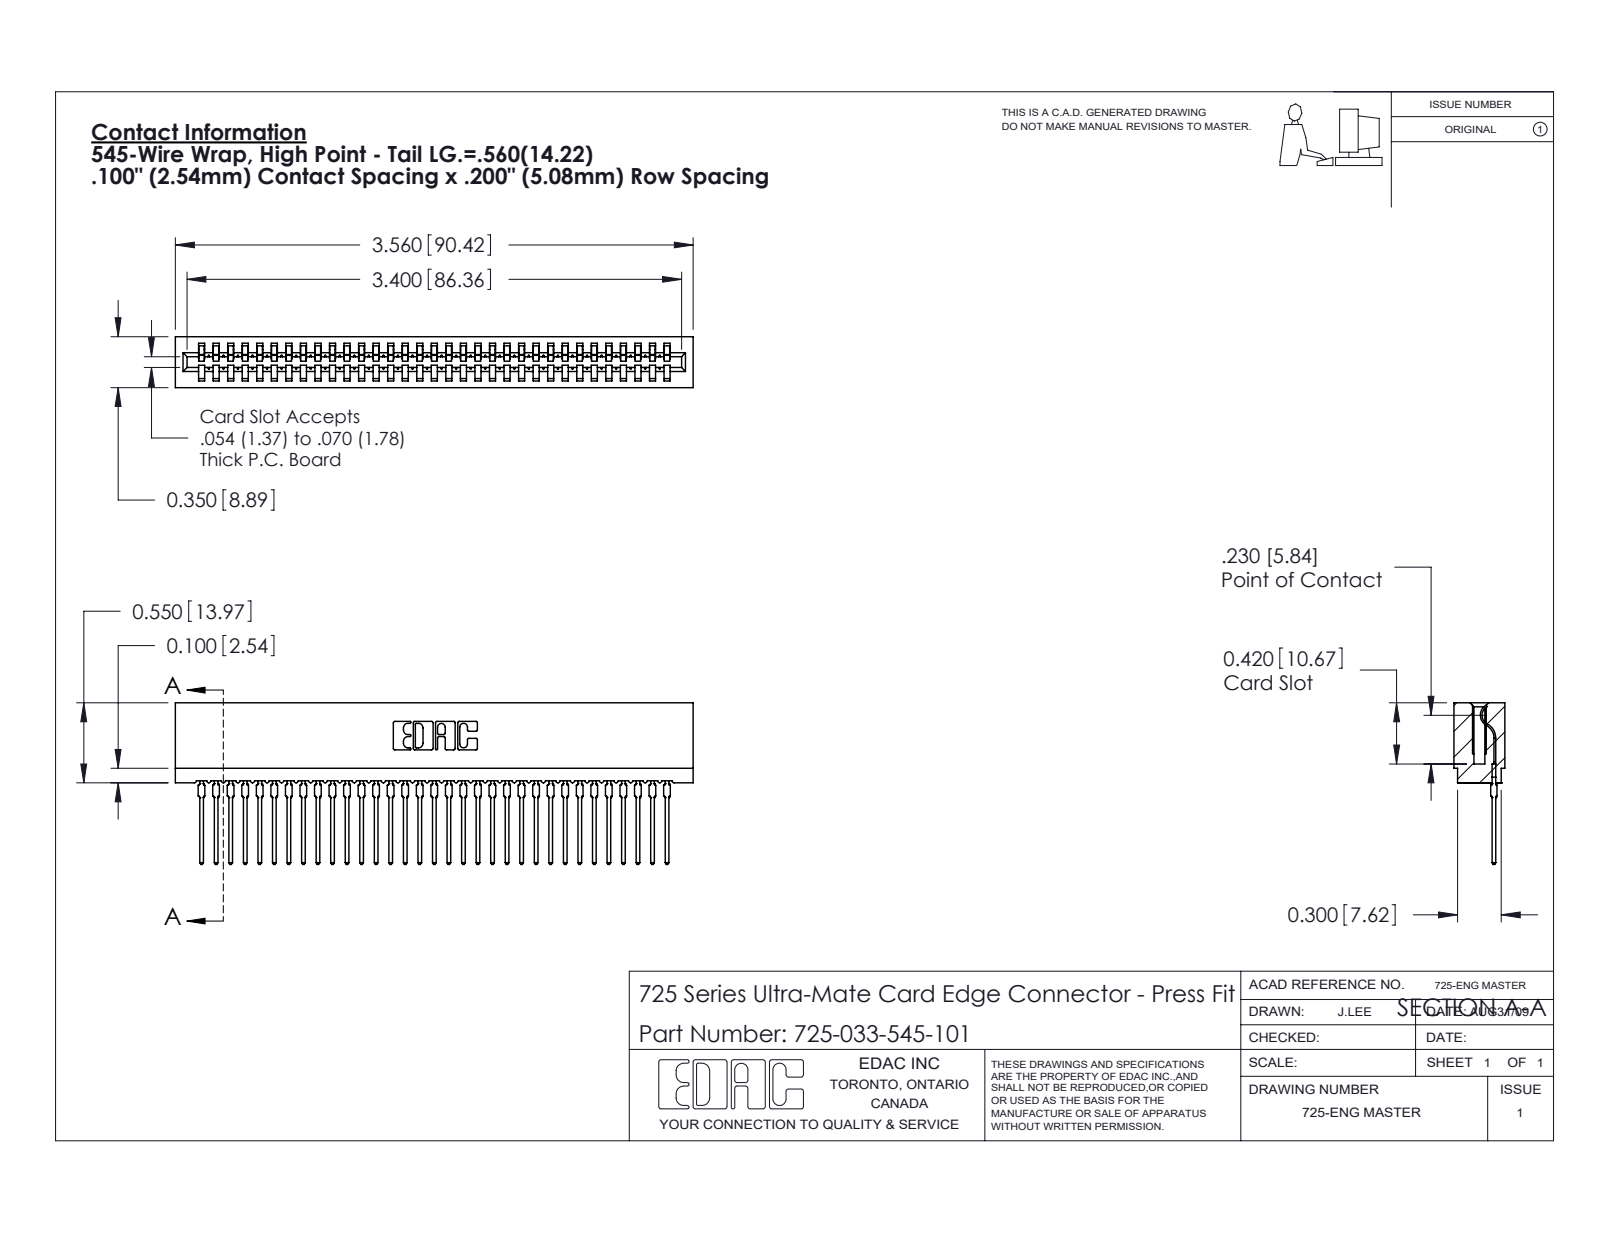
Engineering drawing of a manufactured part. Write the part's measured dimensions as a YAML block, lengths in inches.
part_name: "725 Part_Insulator Option - 01; 745-292-001_545; 725-033-545-101"
step_written_by: "SolidWorks 2020 (CONFIG_CONTROL_DESIGN)"
units: inches
bodies: {solids: 34, faces: 3791, planar: 2266, cylindrical: 667, other: 858}
overall_size: [3.56, 1.111, 0.35]
volume: 0.428
surface_area: 21.41
partial_cylinders:
  - {radius: 0.015, count: 66}
  - {radius: 0.021, count: 66}
  - {radius: 0.01, count: 22}
  - {radius: 0.007, count: 6}
  - {radius: 0.031, count: 6}
  - {radius: 0.005, count: 4}
  - {radius: 0.011, count: 4}
  - {radius: 0.026, count: 3}
face_to_face_distances: [0.2, 0.1, 0.35, 0.3, 0.063, 0.287, 0.212, 0.138, 0.4, 0.5]
